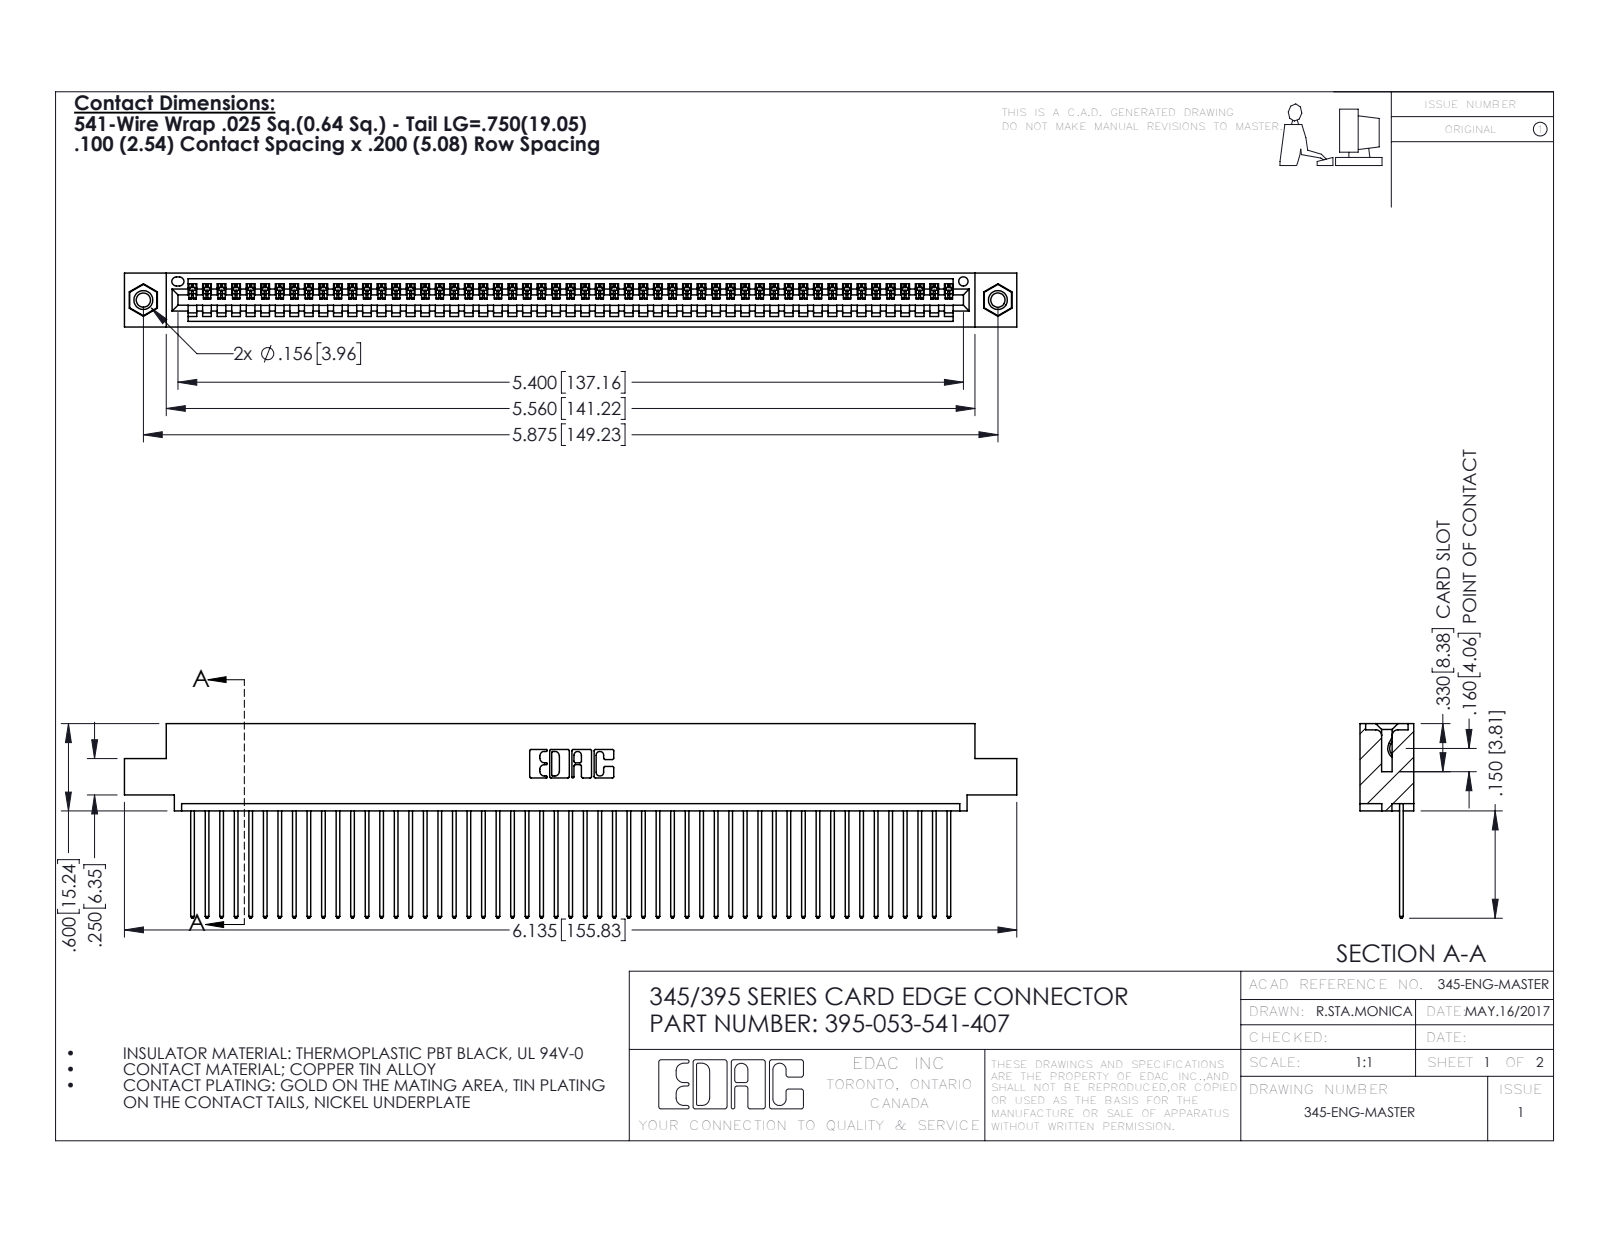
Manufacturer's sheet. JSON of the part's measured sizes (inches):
{"part_name": "395-053-541-407; 345-250-001_345-250-005-103; 345 Part_0.110 Offset - 0.156 Dia-TI; 345-292-001_345-293-141", "step_written_by": "SolidWorks 2016 (CONFIG_CONTROL_DESIGN)", "units": "inches", "bodies": {"solids": 56, "faces": 3264, "planar": 2236, "cylindrical": 1012, "other": 16}, "overall_size": [6.135, 1.337, 0.37], "volume_in3": 0.914, "surface_area_in2": 32.86, "round_holes": [[0.098, 2], [0.125, 2], [0.156, 2], [0.064, 1]], "round_bosses_or_shafts": [[0.155, 2]], "partial_cylinders_radius": [[0.006, 106], [0.01, 106], [0.01, 22], [0.007, 6], [0.031, 6], [0.026, 3], [0.031, 2], [0.04, 2]], "face_to_face_distances": [0.072, 0.298, 0.098, 0.272, 0.025, 0.37, 0.2, 0.225, 0.149, 0.072], "hole_center_spacings": [0.27, 5.639, 5.875]}
